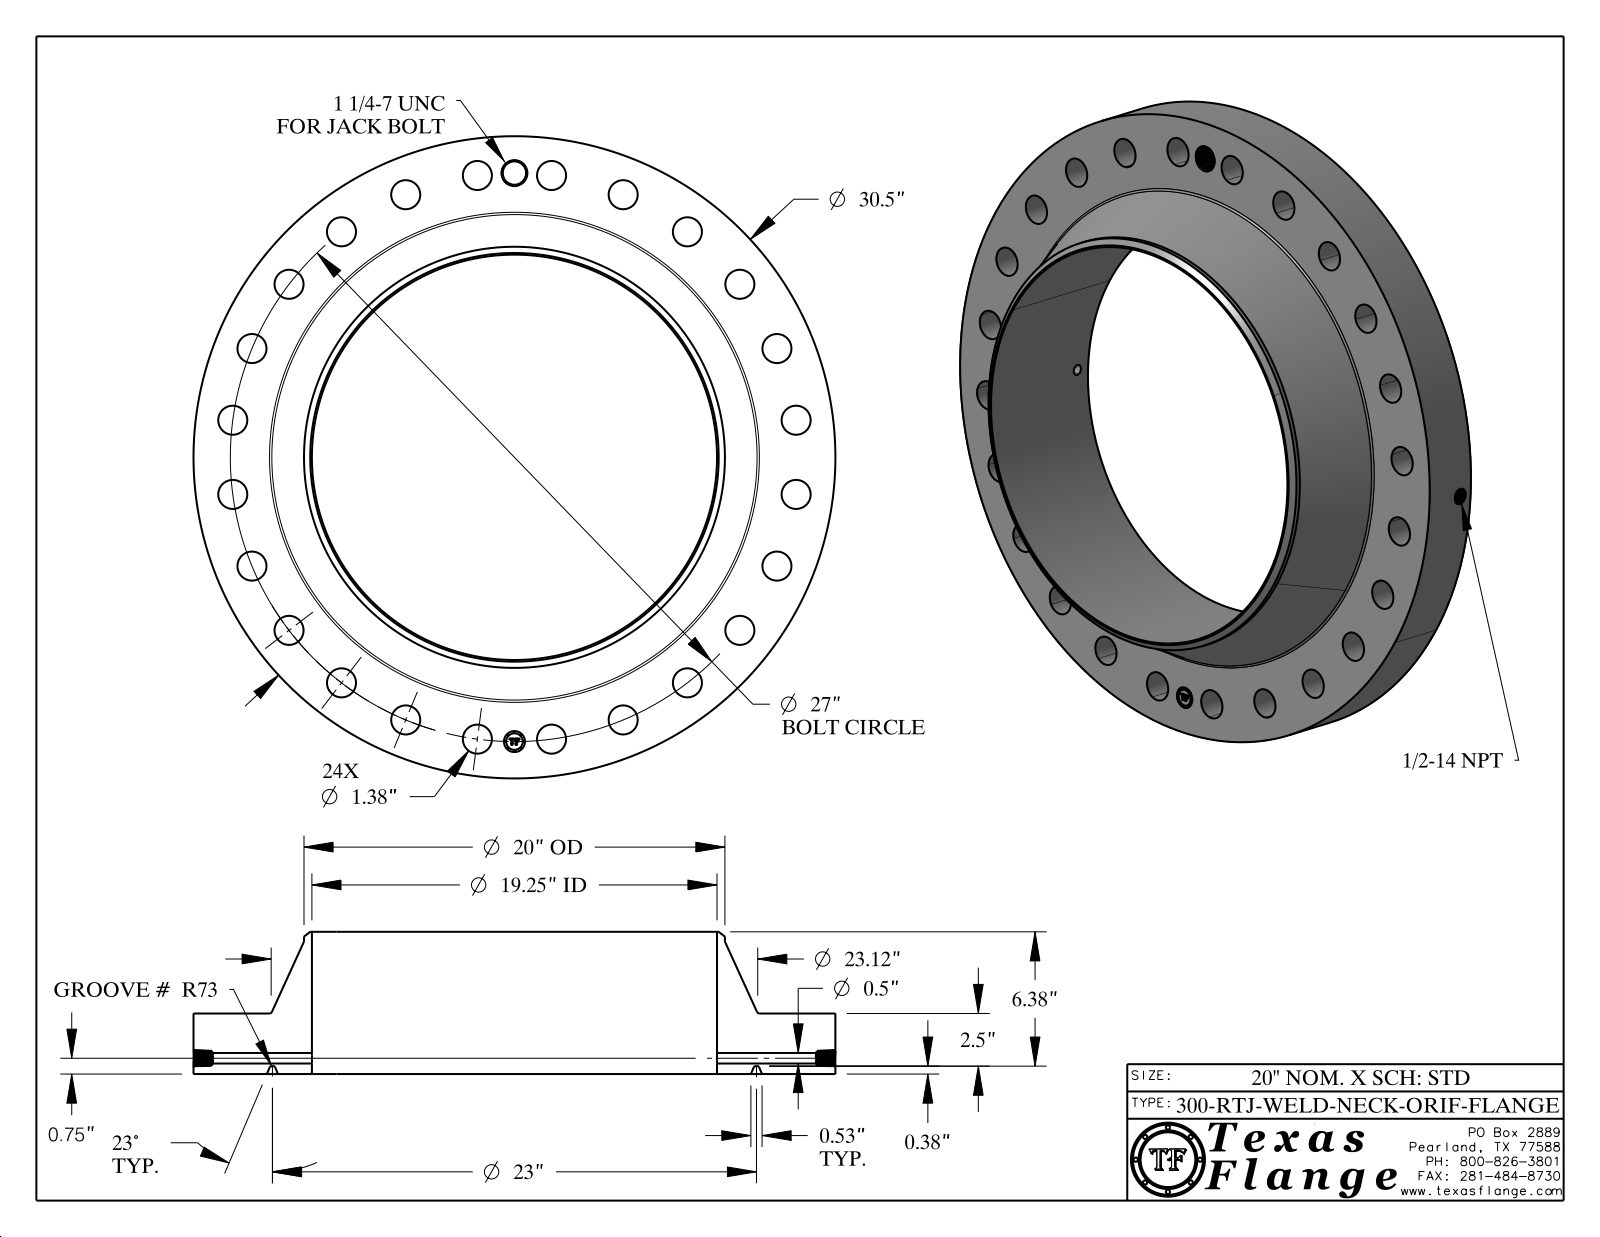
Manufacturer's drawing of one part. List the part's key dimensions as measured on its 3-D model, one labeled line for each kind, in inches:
Part name (STEP PRODUCT): 300-RTJ-WELD-NECK
STEP written by: CATIA V5 STEP AP214 (AUTOMOTIVE_DESIGN)
Units: inches
Bodies: 1 solid, 840 faces (370 planar, 134 cylindrical, 336 other)
Overall size (bounding box): 30.5 × 30.5 × 6.755
Volume: 1 409 in³ · Surface area: 2 026 in²
Round holes (diameter × count): ⌀1.38 ×24, ⌀0.5 ×1, ⌀0.672 ×1, ⌀1 ×1, ⌀1.109 ×1, ⌀19.25 ×1
Round bosses / shafts (diameter × count): ⌀0.061 ×8, ⌀30.5 ×1, ⌀20 ×1, ⌀0.788 ×1
Main face-to-face distances: 2.875, 0.375, 2.5, 6.755, 6.38, 3.88, 0.015, 2.86, 2.485, 3.895
Hole centre spacings: 13.5, 23.383, 24.945, 21.42, 3.524, 6.988, 19.092, 26.08
